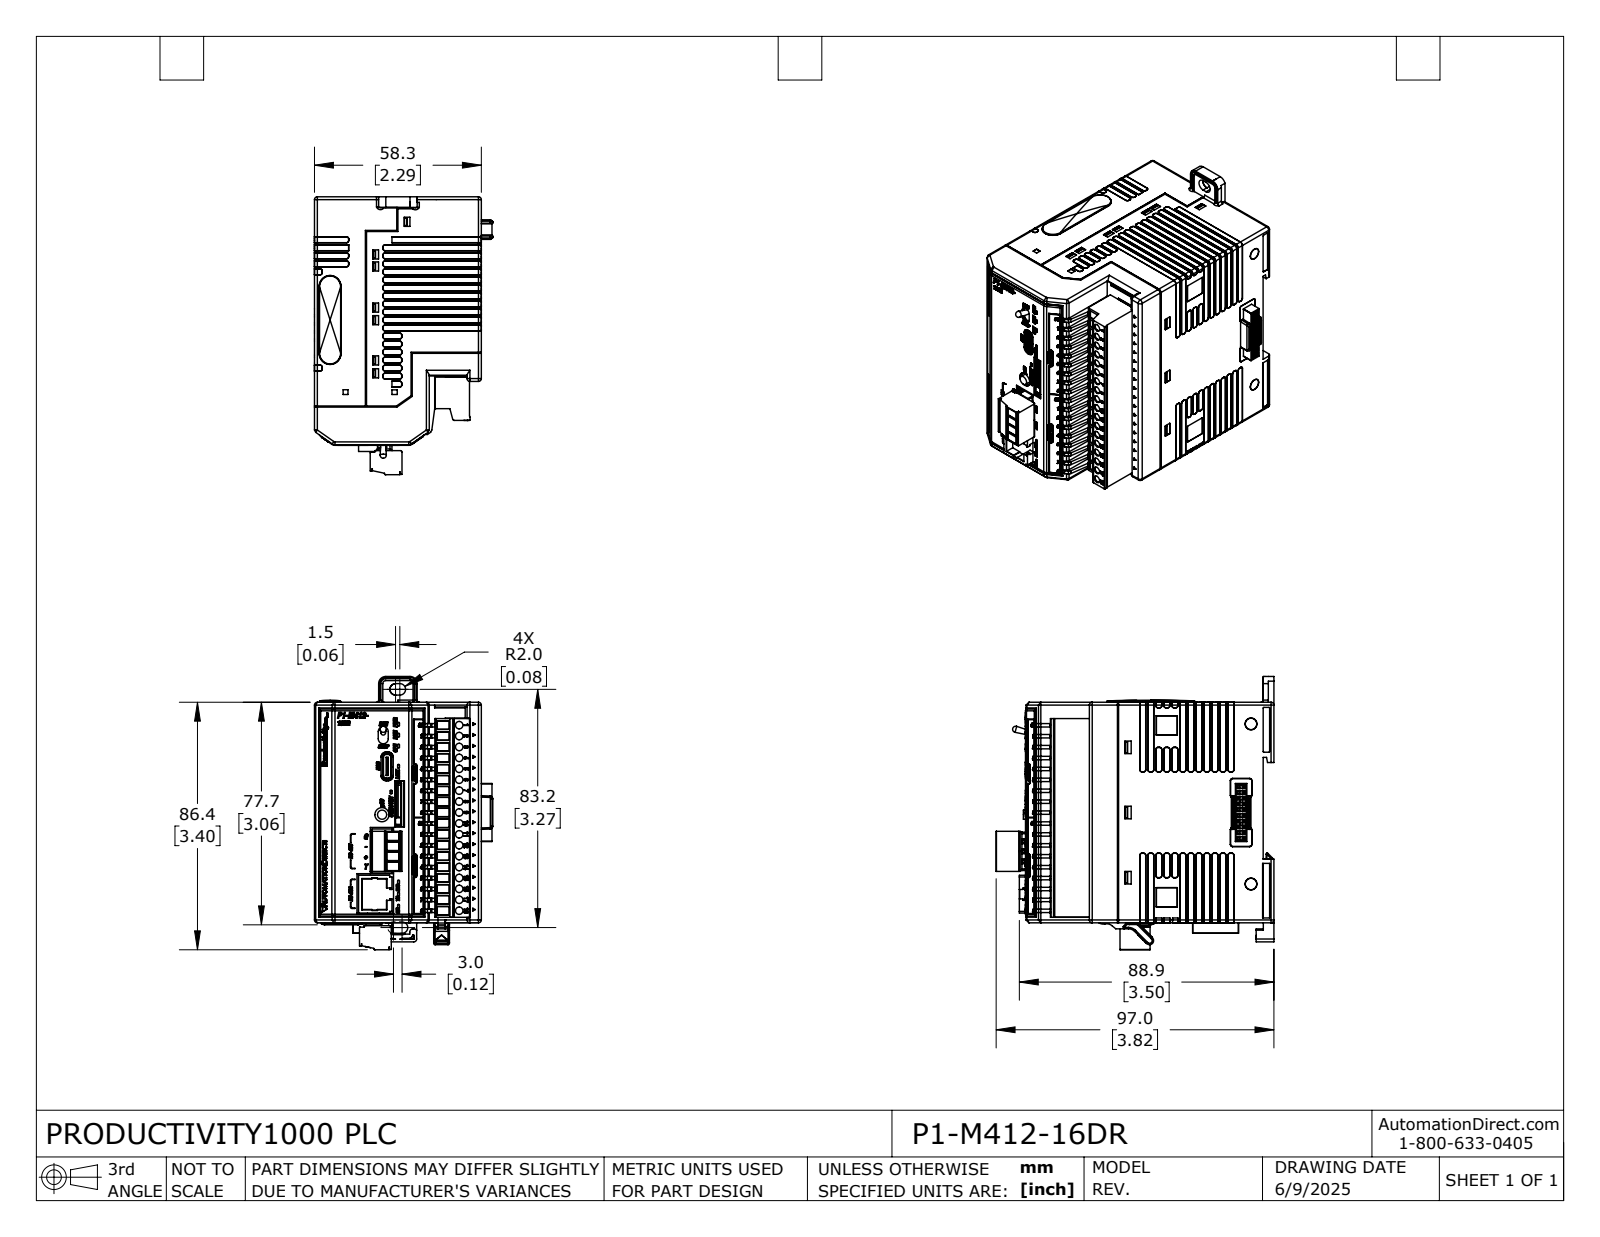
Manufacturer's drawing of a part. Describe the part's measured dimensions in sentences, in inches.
The part is named "P1-M412-16DR". Its 3-D file was written by "SolidWorks 2024 (AUTOMOTIVE_DESIGN)". It is 23 solids with 3639 faces: 2083 planar, 895 cylindrical and 661 other. Overall it measures 3.686 by 3.593 by 2.452 inches. Its volume is 2.099 cubic inches and its surface area 105 square inches. Round holes: 1 of diameter 0.194. Round bosses or shafts: 1 of diameter 0.214, 1 of diameter 0.126. Partial cylindrical surfaces (rounded edges, fillets, slot ends): 172 of radius 0.01, 86 of radius 0.008, 49 of radius 0.02, 33 of radius 0.039, 8 of radius 0.079, 7 of radius 0.024, 6 of radius 0.004, 4 of radius 0.012. The main face-to-face distances are 2.235, 0.02, 0.039, 2.275, 3.01, 3.022, 2.294, 2.294, 2.255, 3.02.
